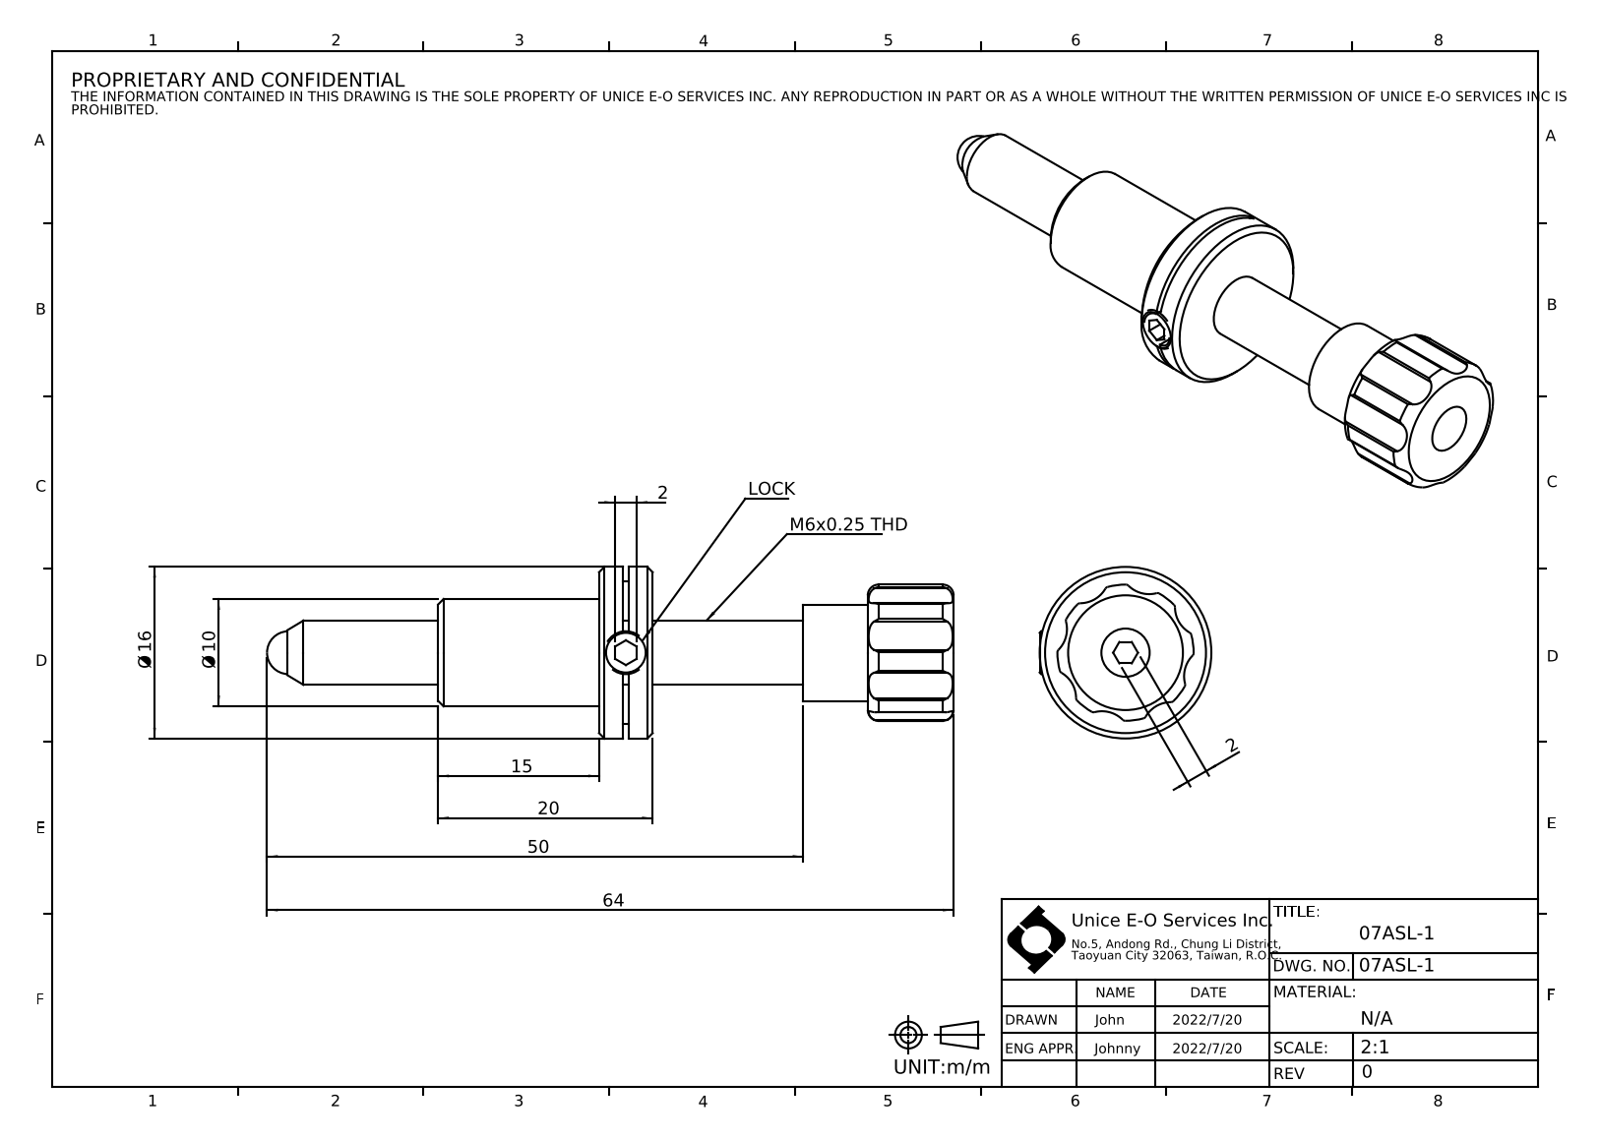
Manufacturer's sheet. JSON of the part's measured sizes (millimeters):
{"part_name": "07ASL-1", "step_written_by": "SolidWorks 2021 (CONFIG_CONTROL_DESIGN)", "units": "millimeters", "bodies": {"solids": 5, "faces": 116, "planar": 27, "cylindrical": 58, "other": 31}, "overall_size": [64, 16, 16], "volume_mm3": 4236, "surface_area_mm2": 3780, "round_holes": [[3.3, 1], [4, 1], [4.5, 1], [5, 1], [5.9, 1]], "round_bosses_or_shafts": [[16, 1], [10, 1], [9, 1], [6, 1], [4, 1]], "partial_cylinders_radius": [[0.3, 16], [2.75, 8], [6.35, 1]], "face_to_face_distances": [2.25, 2.75, 0.5, 5, 33.05, 30.8, 30.3, 28.05, 25.05, 22.8]}
